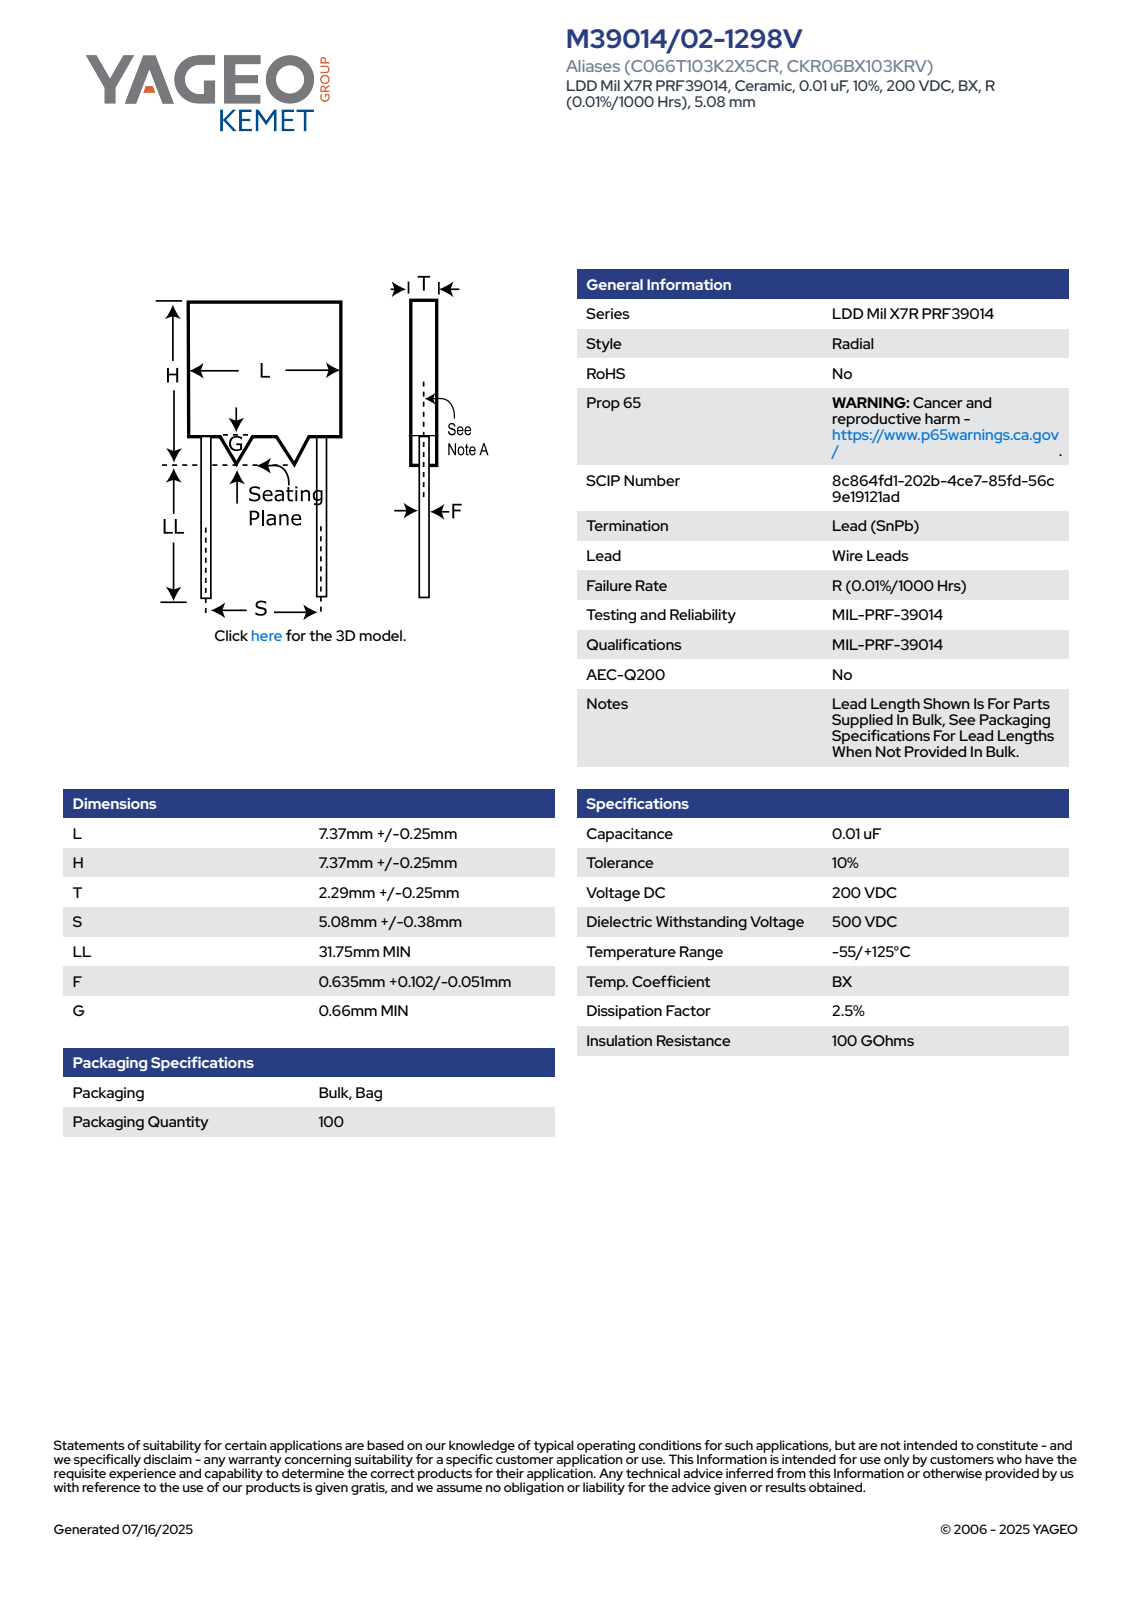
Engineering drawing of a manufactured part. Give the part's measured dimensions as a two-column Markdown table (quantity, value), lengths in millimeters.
| quantity | value |
| --- | --- |
| part name | CCRM_V_C066_L7.62H8.026T2.54S5.08LL31.75F0.737G0.66 |
| STEP written by | SolidWorks 2014 (AUTOMOTIVE_DESIGN) |
| units | millimeters |
| bodies | 4 solids, 75 faces (71 planar, 4 cylindrical, 0 other) |
| overall size | 38.87 × 7.62 × 2.54 |
| volume | 168 mm³ |
| surface area | 346 mm² |
| round bosses / shafts (diameter × count) | 0.74 × 2 |
| main face-to-face distances | 2.54, 7.62, 7.12, 2.01, 31.75, 38.87, 1.21, 35.7, 3.95, 3.17 |
